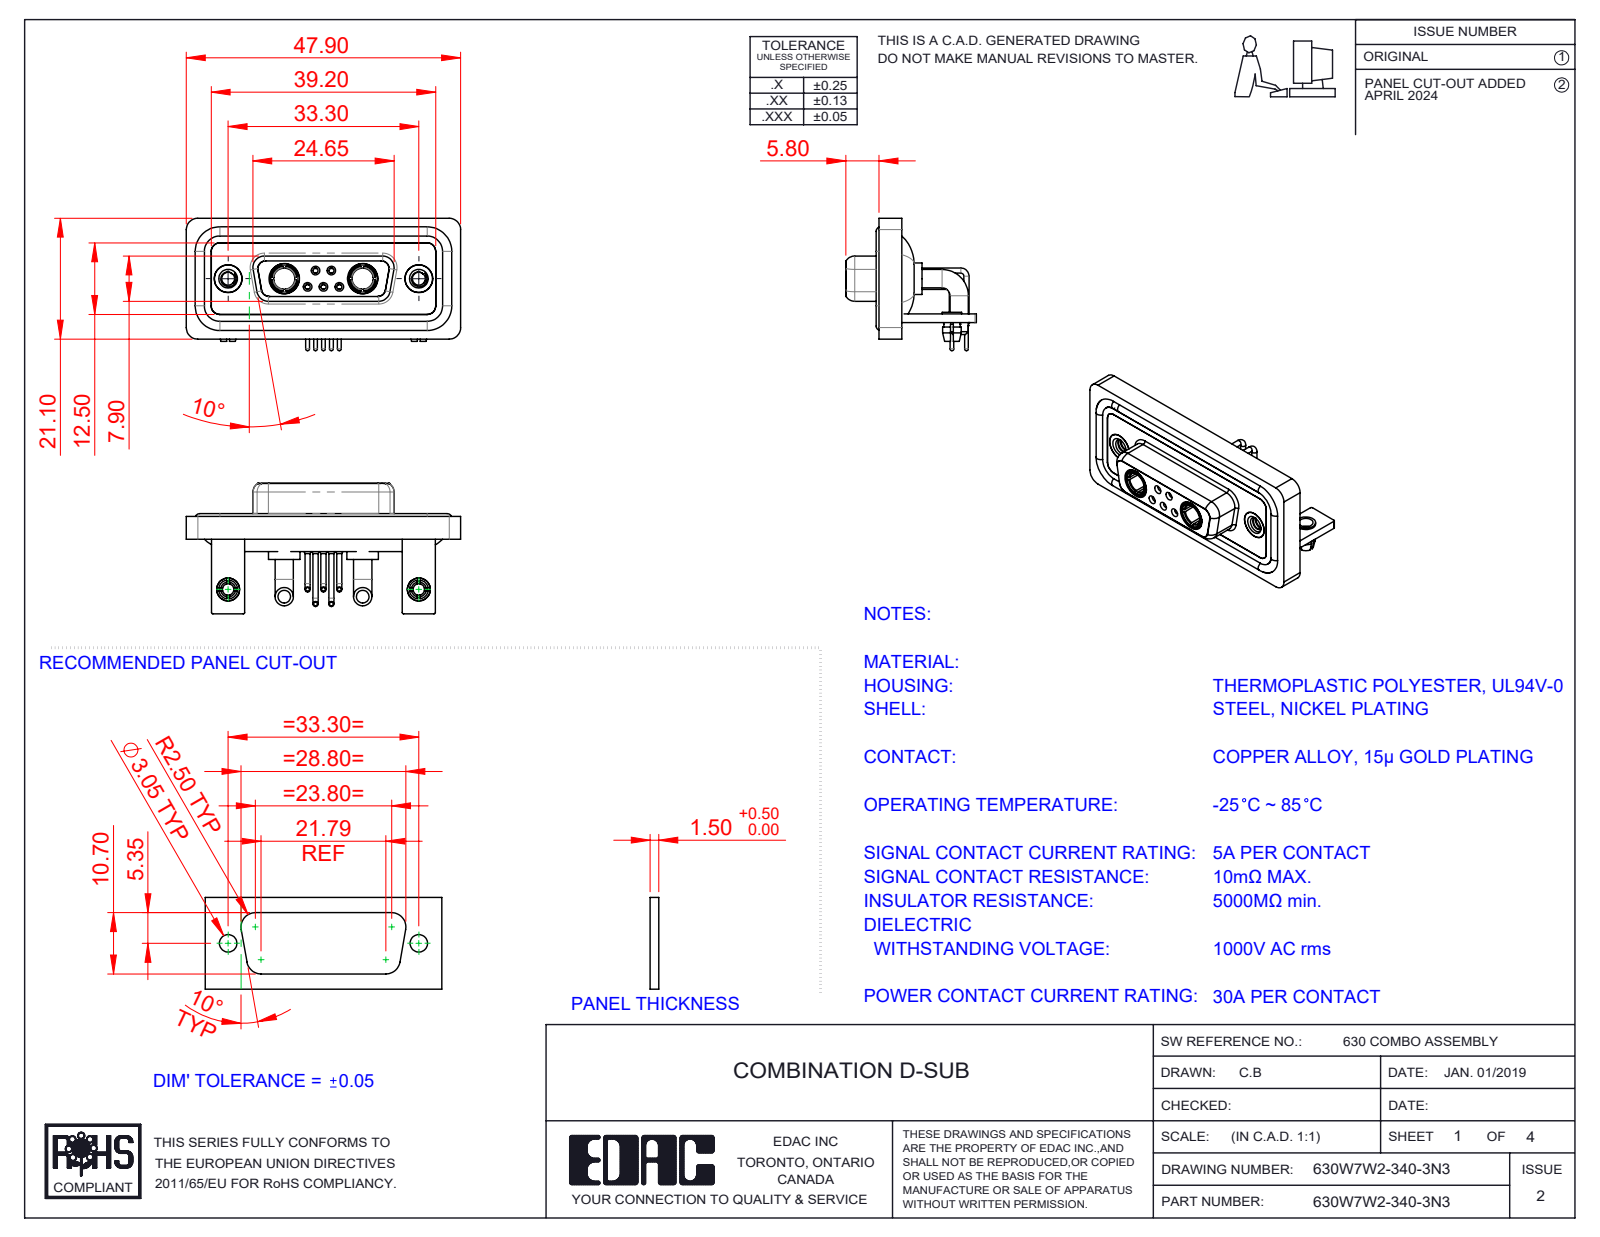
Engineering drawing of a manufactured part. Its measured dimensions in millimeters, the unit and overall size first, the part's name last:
Units: millimetres
Overall size (bounding box): 47.9 × 23.12 × 22.8
Round holes (diameter × count): ⌀2 ×7, ⌀0.9 ×5, ⌀1.1 ×5, ⌀1.5 ×5, ⌀4.85 ×4, ⌀1.6 ×3, ⌀1.7 ×2, ⌀2.26 ×2, ⌀2.5 ×2, ⌀3.2 ×2, ⌀3.7 ×2, ⌀4 ×2
Round bosses / shafts (diameter × count): ⌀1.6 ×6, ⌀0.9 ×5, ⌀0.65 ×5, ⌀3.2 ×4, ⌀5.5 ×2, ⌀5.2 ×2, ⌀4.96 ×2, ⌀4.95 ×2
Partial cylindrical surfaces — rounded edges, fillets, slot ends (radius × count): R2 ×21, R1.5 ×18, R0.25 ×16, R1.35 ×12, R1.6 ×8, R0.5 ×5, R0.6 ×4, R0.65 ×4
Main face-to-face distances: 0.4, 2.9, 1.5, 1.8, 3.7, 1.1, 4.1, 1.6, 2.5, 1.4
Hole centre spacings: 3.16, 2.77, 9.8, 23.5, 33.3, 4.31, 4.33, 5.03
Volume: 6 655 mm³ · Surface area: 11 188 mm²
Bodies: 20 solids, 947 faces (306 planar, 409 cylindrical, 232 other)
Part name (STEP PRODUCT): 630Combo Threaded Rivet_2; 630Combo Shell Rear_15 Contacts; 630Combo Stabilizer Bracket_50 Contacts; 630Combo Contact Row 2_50 Contacts (+7 more)
STEP written by: SolidWorks 2023 (CONFIG_CONTROL_DESIGN)
